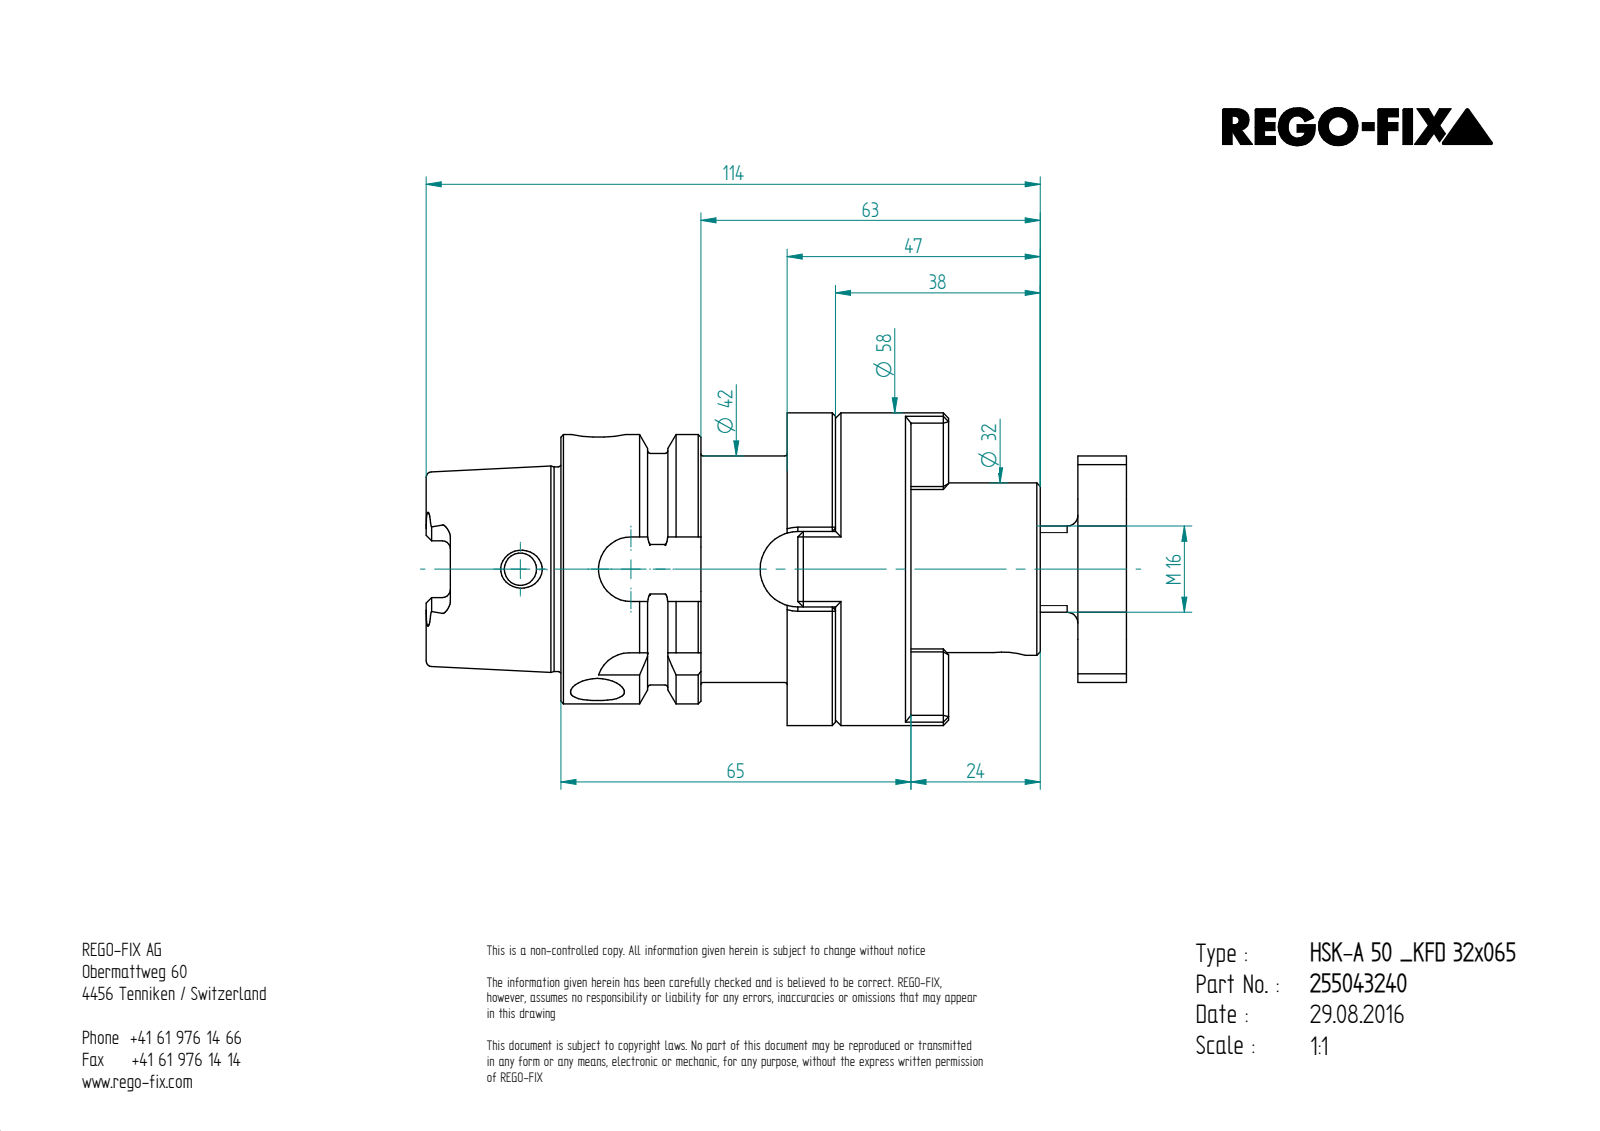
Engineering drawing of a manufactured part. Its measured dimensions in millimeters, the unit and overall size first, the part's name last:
Units: millimetres
Overall size (bounding box): 130 × 58 × 58
Round holes (diameter × count): ⌀10 ×2, ⌀6 ×1, ⌀6.8 ×1, ⌀6.96 ×1, ⌀13.84 ×1, ⌀14.92 ×1, ⌀17 ×1, ⌀26 ×1, ⌀32 ×1
Round bosses / shafts (diameter × count): ⌀58 ×1, ⌀50 ×1, ⌀43 ×1, ⌀42 ×1, ⌀38.01 ×1, ⌀31.4 ×1, ⌀16 ×1
Partial cylindrical surfaces — rounded edges, fillets, slot ends (radius × count): R1.5 ×6, R2.38 ×4, R5 ×4, R6 ×4, R4 ×2, R7 ×1
Main face-to-face distances: 63, 16, 40, 23, 9, 54, 31, 7, 24, 45
Volume: 159 158 mm³ · Surface area: 33 903 mm²
Bodies: 1 solid, 278 faces (143 planar, 55 cylindrical, 80 other)
STEP written by: Unknown (AUTOMOTIVE_DESIGN)
